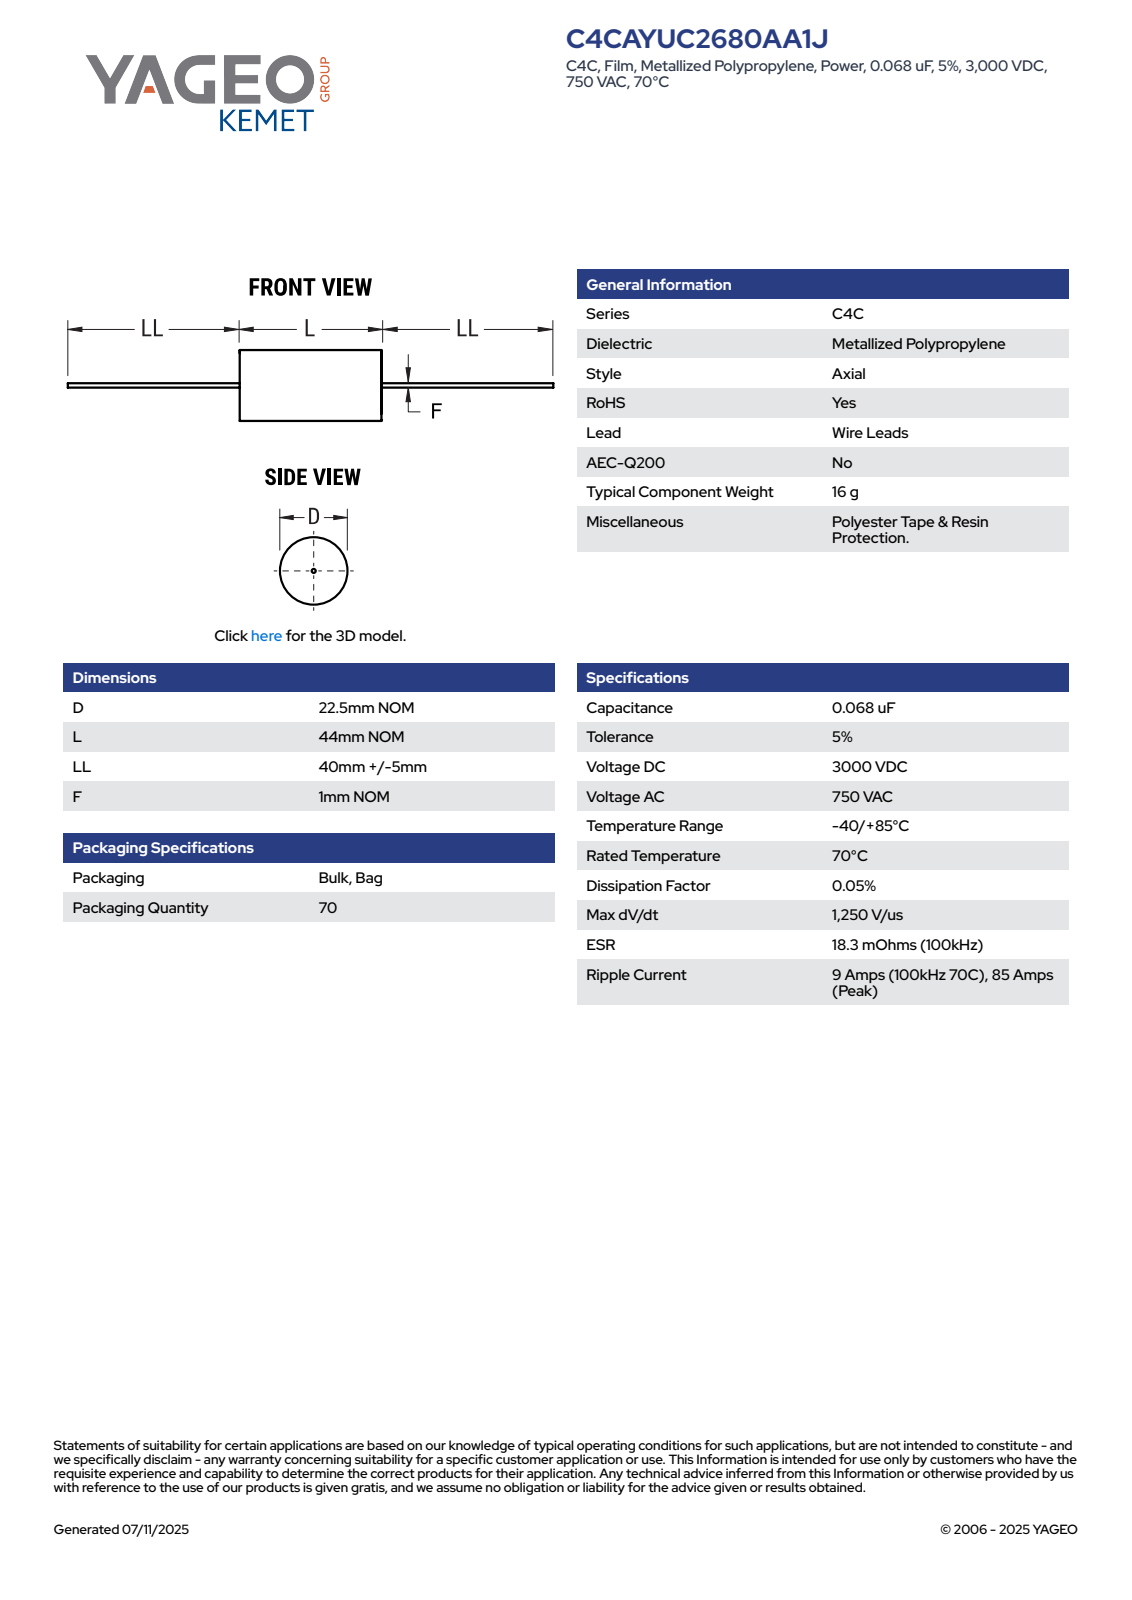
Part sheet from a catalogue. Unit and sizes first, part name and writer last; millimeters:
Units: millimetres
Overall size (bounding box): 134 × 22.5 × 22.5
Round bosses / shafts (diameter × count): ⌀22.5 ×1, ⌀1 ×1
Partial cylindrical surfaces — rounded edges, fillets, slot ends (radius × count): R11.24 ×1
Main face-to-face distances: 44, 43.99, 44.99, 45, 88.99, 134, 89.01, 89, 45.01
Volume: 17 565 mm³ · Surface area: 4 983 mm²
Bodies: 2 solids, 87 faces (28 planar, 28 cylindrical, 31 other)
Part name (STEP PRODUCT): CFP_ACWF_22.5X44_D22.5L44LL45F1
STEP written by: SolidWorks 2014 (AUTOMOTIVE_DESIGN)
